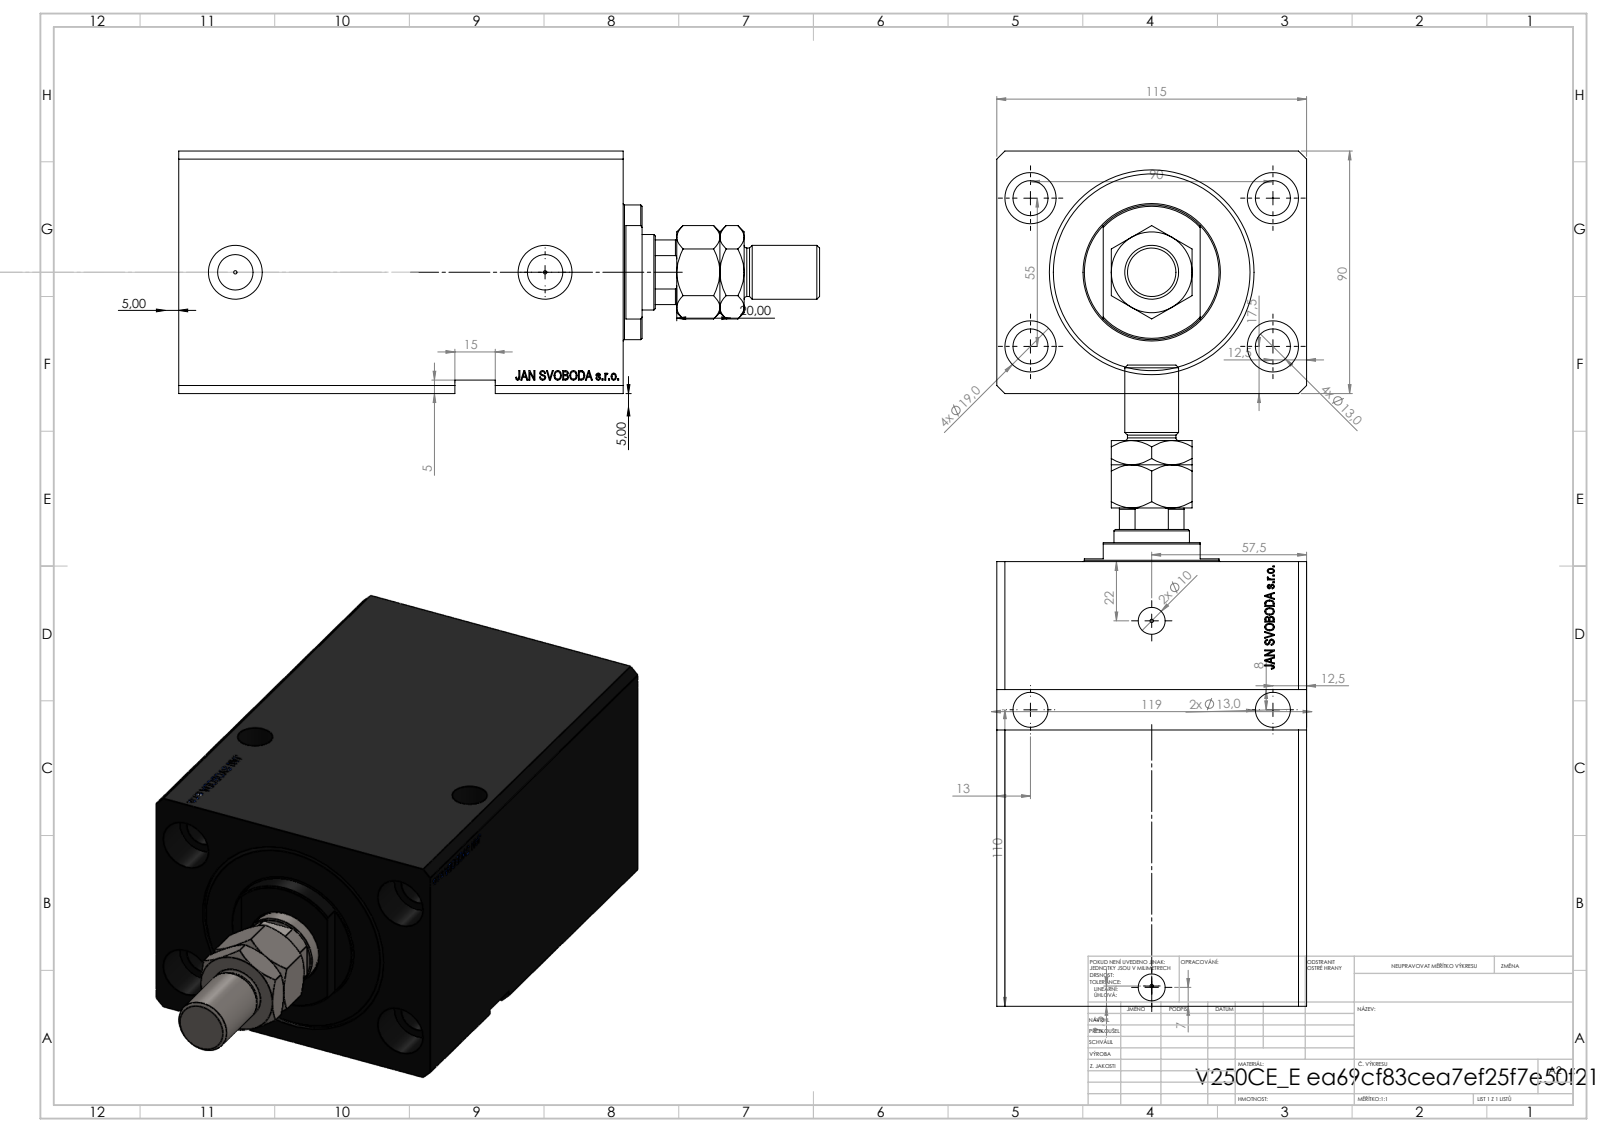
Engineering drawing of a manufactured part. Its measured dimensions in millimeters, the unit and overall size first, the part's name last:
Units: millimetres
Overall size (bounding box): 238 × 115 × 90
Round holes (diameter × count): ⌀13 ×6, ⌀1.25 ×4, ⌀19 ×4, ⌀8.5 ×2, ⌀10 ×2, ⌀13.16 ×2, ⌀20 ×2, ⌀18.5 ×1, ⌀28 ×1, ⌀63 ×1, ⌀76 ×1
Round bosses / shafts (diameter × count): ⌀50 ×1, ⌀20 ×1, ⌀18 ×1
Partial cylindrical surfaces — rounded edges, fillets, slot ends (radius × count): R13.5 ×1
Main face-to-face distances: 90, 115, 20, 165, 17.9, 147.1, 145, 127.1, 65, 80
Hole centre spacings: 52.74, 90, 29.73, 55, 55.8, 60.42, 73.38, 84.26
Volume: 1 403 000 mm³ · Surface area: 203 409 mm²
Bodies: 4 solids, 994 faces (482 planar, 96 cylindrical, 416 other)
Part name (STEP PRODUCT): V250CE_E_Body; V250CE_C_VCP; V250CE_VC_E; MTA
STEP written by: SolidWorks 2019 (CONFIG_CONTROL_DESIGN)
